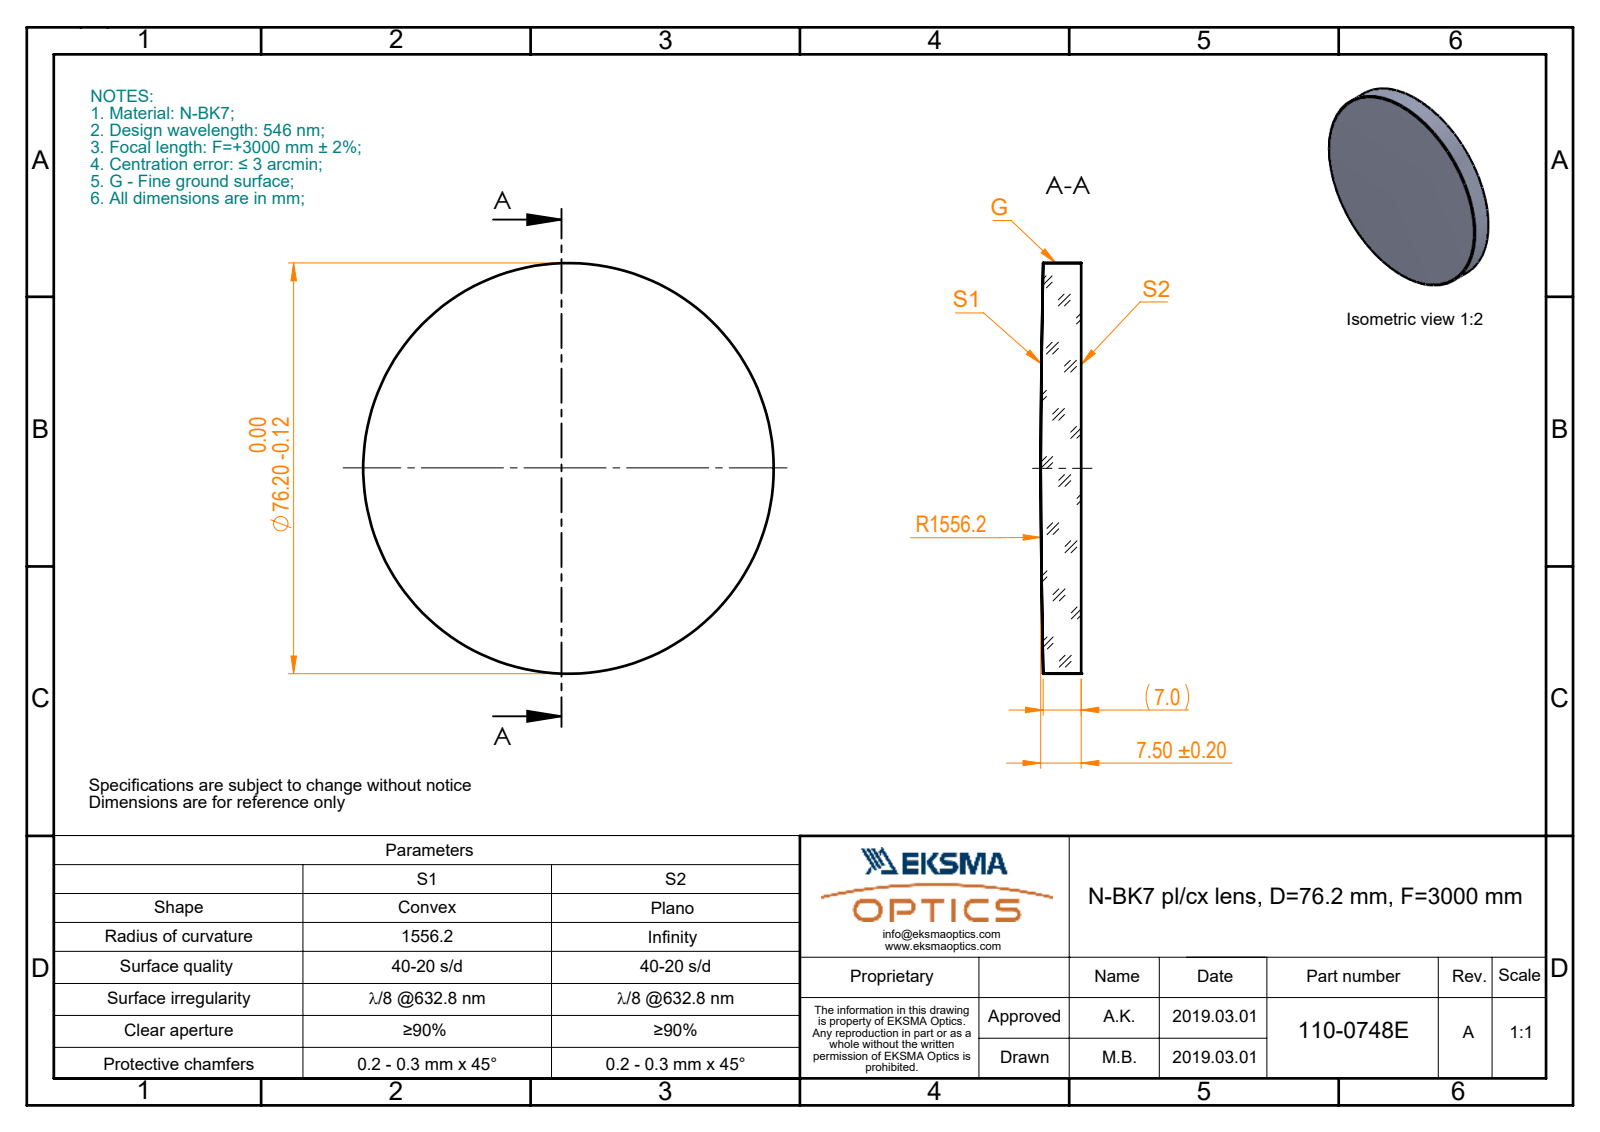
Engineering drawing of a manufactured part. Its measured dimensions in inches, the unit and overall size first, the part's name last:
Units: inches
Overall size (bounding box): 3 × 3 × 0.295
Round bosses / shafts (diameter × count): ⌀3 ×1
Volume: 2.022 in³ · Surface area: 16.75 in²
Bodies: 1 solid, 5 faces (1 planar, 2 cylindrical, 2 other)
Part name (STEP PRODUCT): 110-0748E BK7 pl-cx 76.2 F3000
STEP written by: SolidWorks 2017 (CONFIG_CONTROL_DESIGN)
